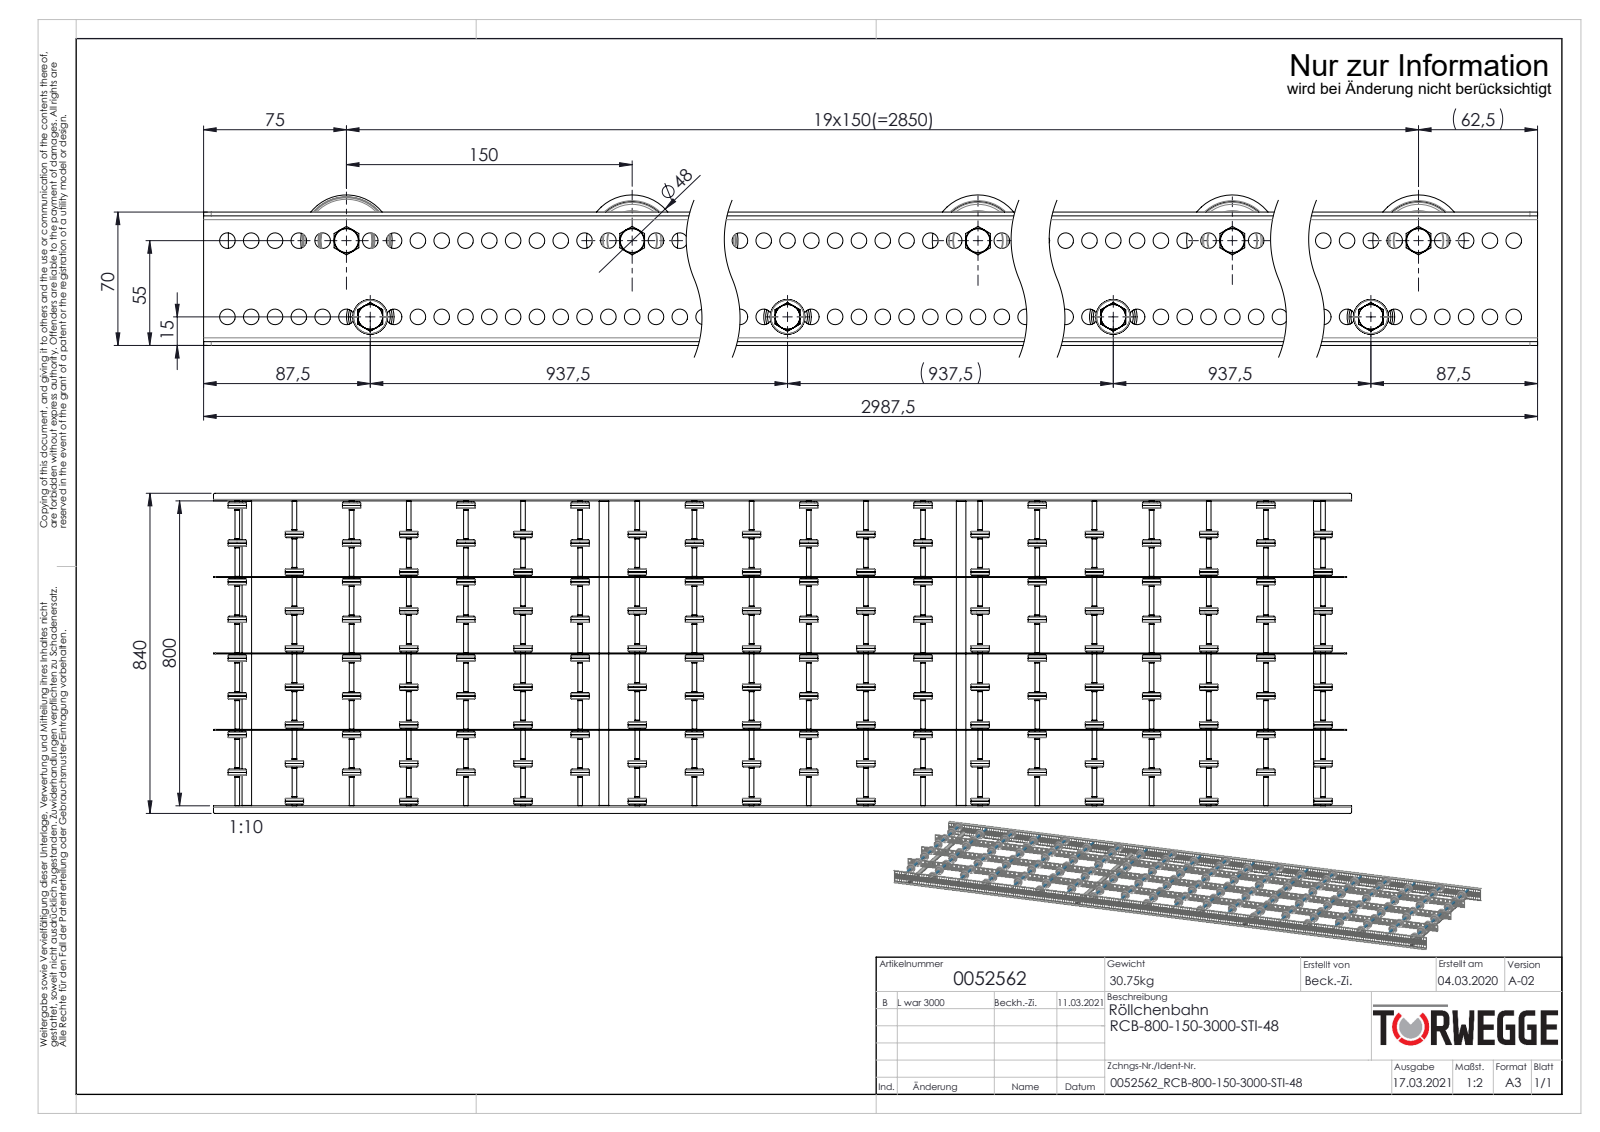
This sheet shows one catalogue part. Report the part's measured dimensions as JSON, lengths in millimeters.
{"part_name": "Röllchenachse-für-Konfiguration_EL800 Stahl; 0052562; 0046278_KB-ROHR-12X1,75mm_KFG_L75; S100994_Sperrzahnschraube_M08x16-8.8-A2K (+6 more)", "step_written_by": "SolidWorks 2020 (AUTOMOTIVE_DESIGN)", "units": "millimeters", "bodies": {"solids": 565, "faces": 18196, "planar": 3462, "cylindrical": 7726, "other": 7008}, "overall_size": [2987.5, 840, 79], "volume_mm3": 7232000, "surface_area_mm2": 5713000, "round_holes": [[8.2, 476], [8.5, 119], [6.65, 20], [8, 20], [9.65, 20], [15, 20], [41, 20], [6.8, 4], [21, 4]], "round_bosses_or_shafts": [[48, 20], [13, 20], [12.5, 20], [12.4, 20], [12, 20], [11.5, 20], [25, 4], [8, 4]], "partial_cylinders_radius": [[4, 8], [2, 4], [5, 4]], "face_to_face_distances": [200.5, 401, 2, 203, 2.5, 198, 802, 601.5, 403.5, 398.5], "hole_center_spacings": [12.5, 25, 37.5, 50, 62.5, 75, 87.5, 100]}
